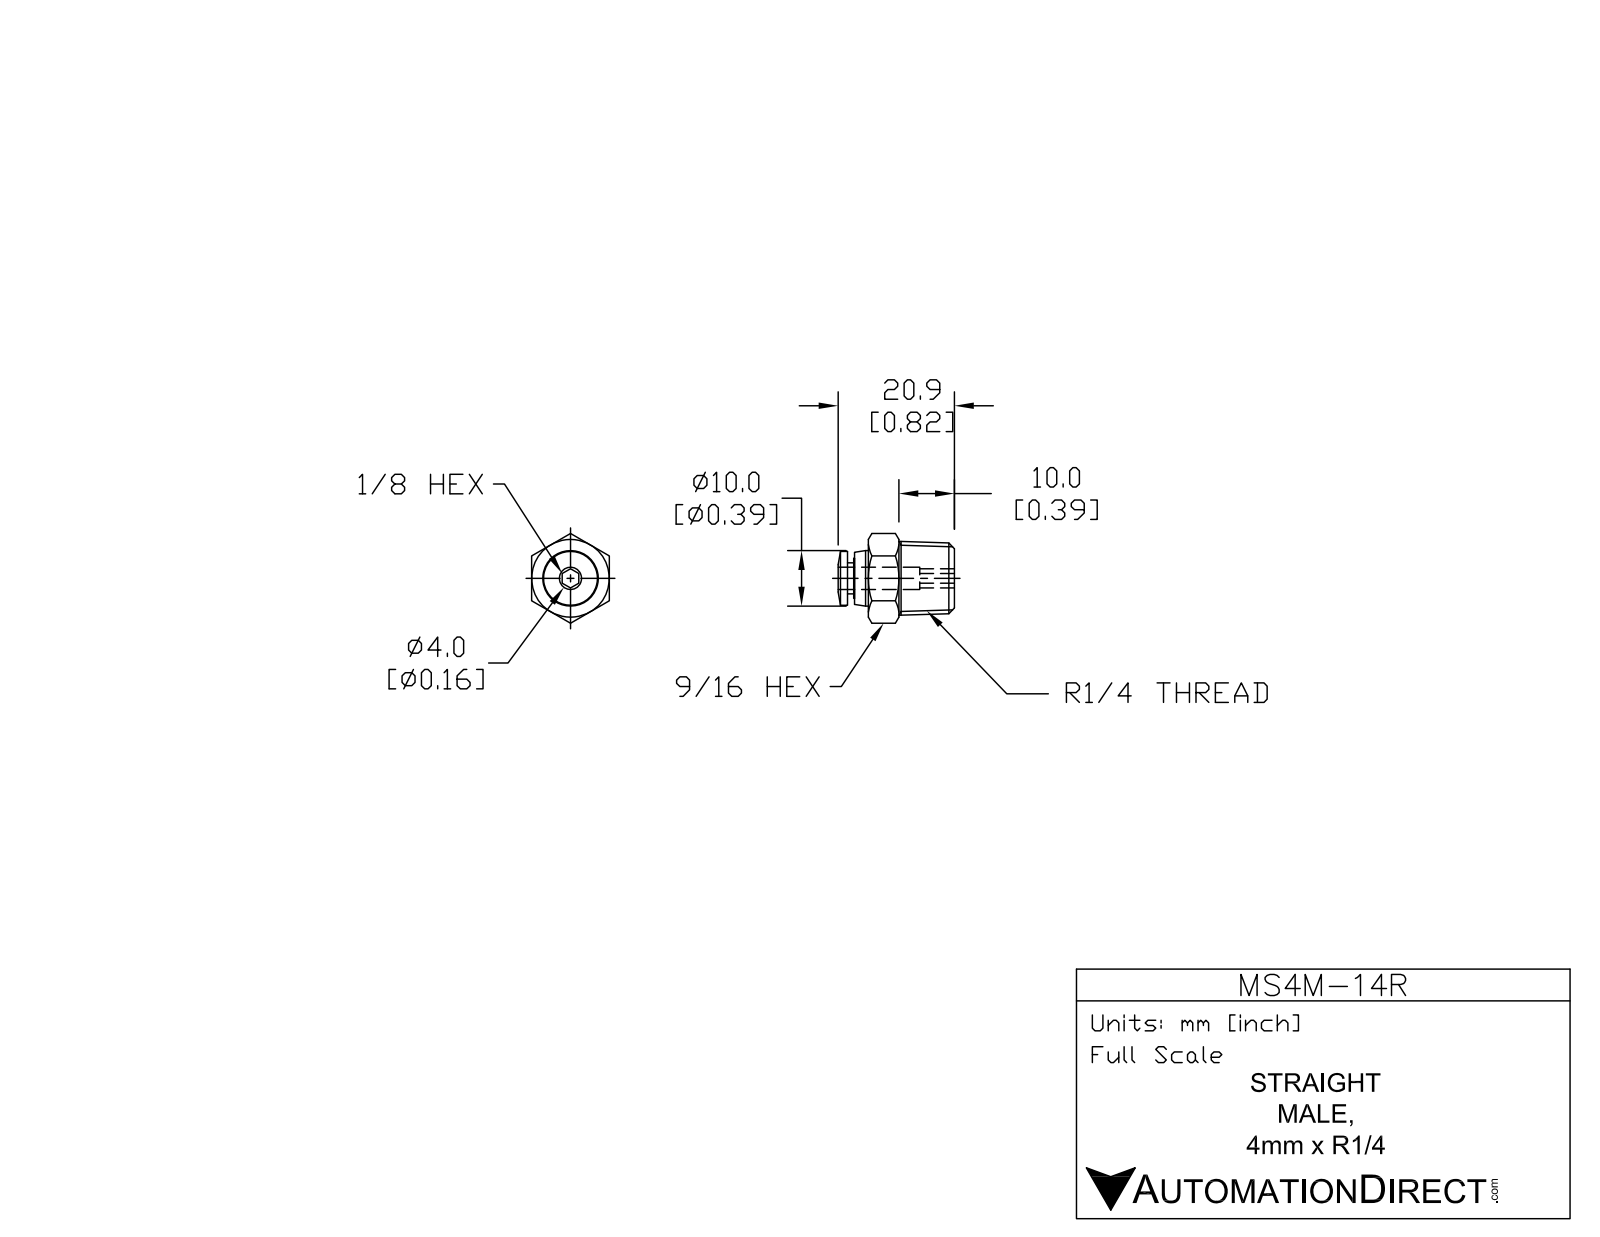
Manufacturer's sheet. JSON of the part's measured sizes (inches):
{"part_name": "MS4M-14R", "step_written_by": "SolidWorks 2015 (AUTOMOTIVE_DESIGN)", "units": "inches", "bodies": {"solids": 1, "faces": 50, "planar": 14, "cylindrical": 12, "other": 24}, "overall_size": [0.825, 0.636, 0.551], "volume_in3": 0.14, "surface_area_in2": 2.229, "round_holes": [[0.138, 1], [0.169, 1]], "round_bosses_or_shafts": [[0.394, 1], [0.382, 1], [0.283, 1], [0.22, 1]], "face_to_face_distances": [0.551, 0.61, 0.148, 0.758, 0.709, 0.098, 0.049, 0.364, 0.715, 0.104]}
